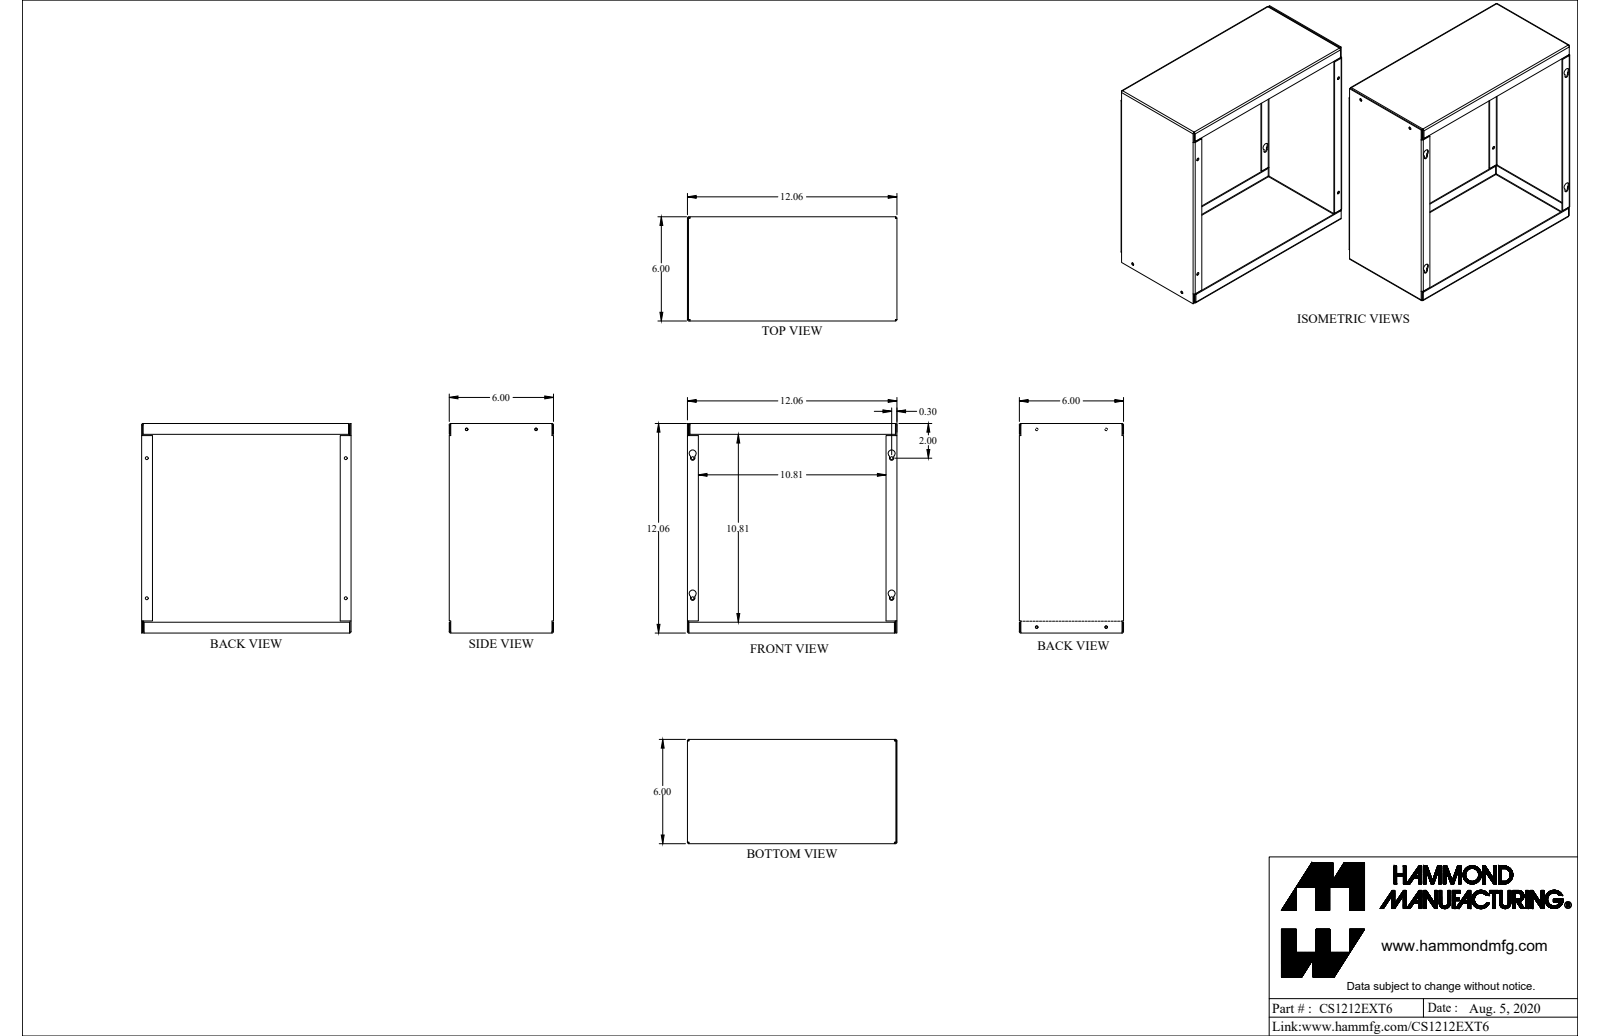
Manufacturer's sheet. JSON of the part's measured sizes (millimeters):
{"part_name": "CS1212EXT6", "step_written_by": "SolidWorks 2021 (AUTOMOTIVE_DESIGN)", "units": "millimeters", "bodies": {"solids": 2, "faces": 124, "planar": 80, "cylindrical": 44, "other": 0}, "overall_size": [306.4, 306.4, 152.4], "volume_mm3": 319900, "surface_area_mm2": 447000, "round_holes": [[3.7, 4], [4.3, 4]], "round_bosses_or_shafts": [[3.3, 4]], "partial_cylinders_radius": [[0.7, 12], [2.2, 12], [3.2, 4], [5.2, 4]], "face_to_face_distances": [305, 1.4, 1.4, 303.5, 306.4, 306.4, 303.5, 151, 152.4, 149.5], "hole_center_spacings": [101.6, 204.8, 289.1, 291.1, 306.4, 355.9]}
